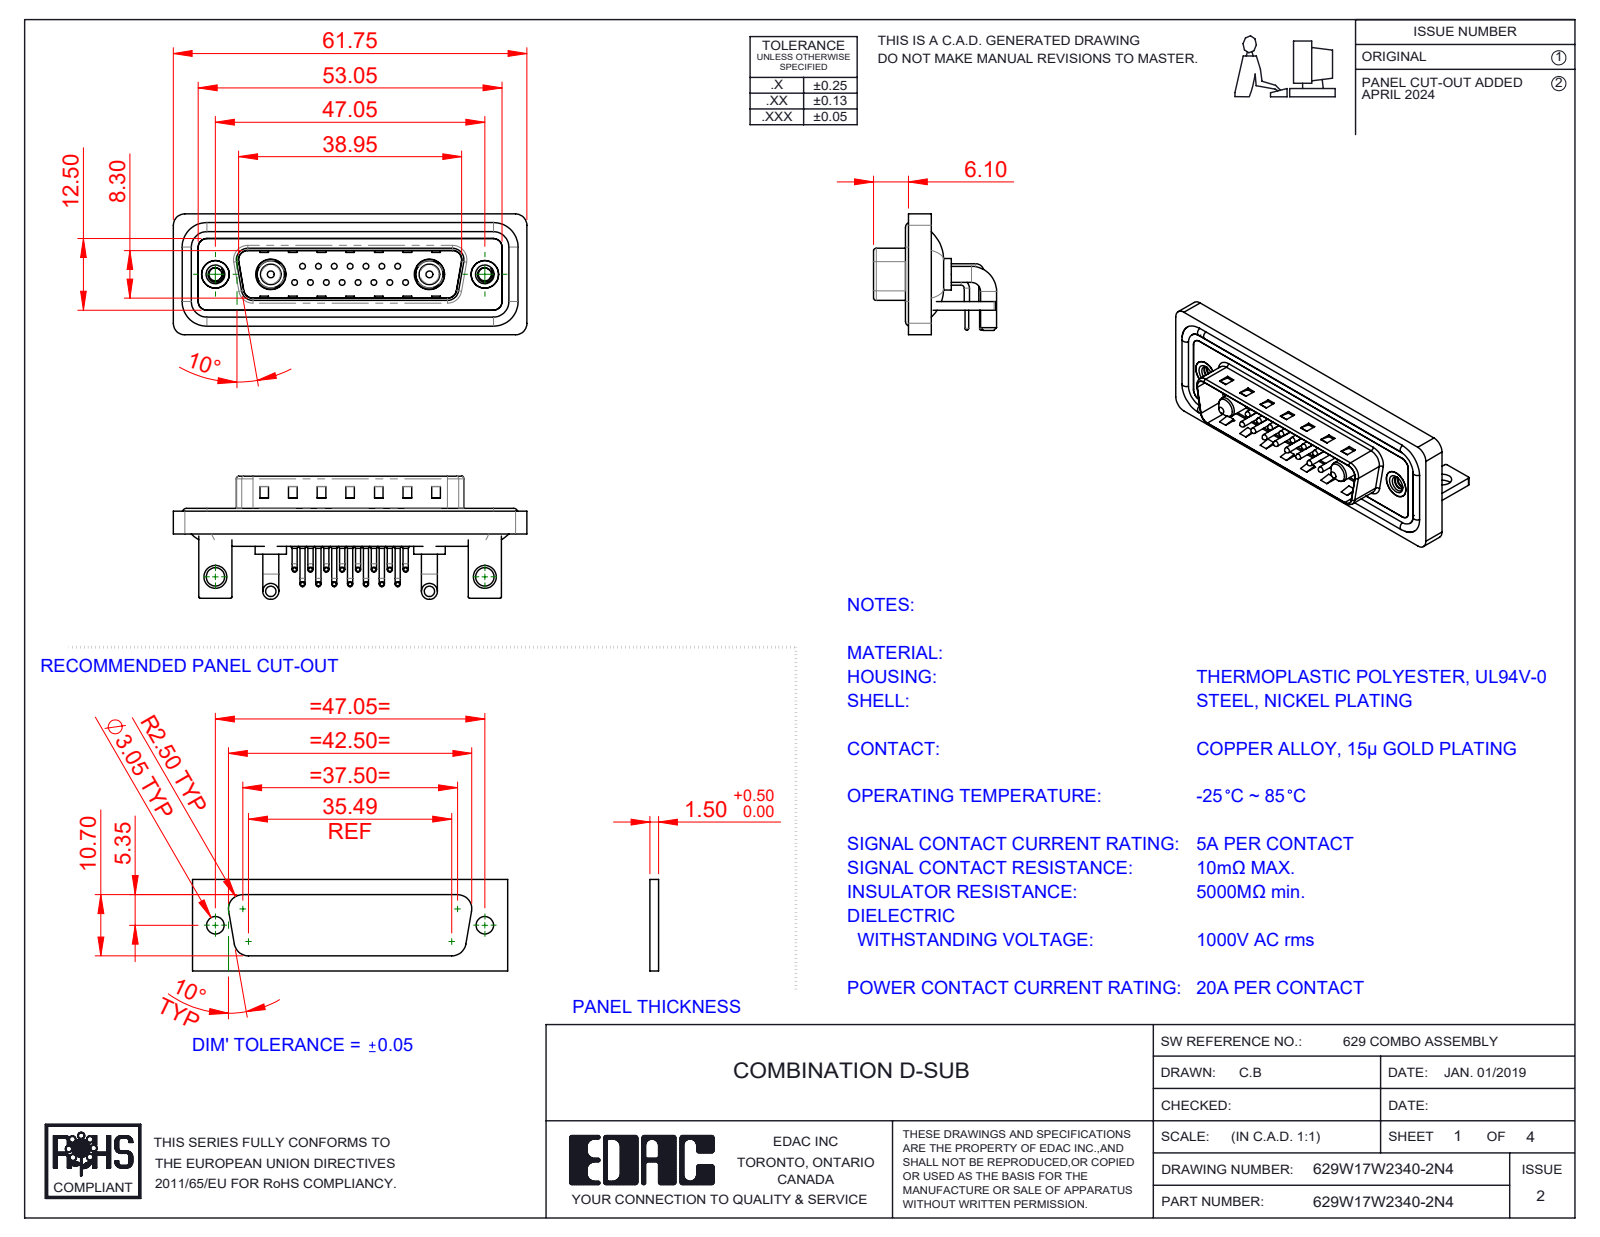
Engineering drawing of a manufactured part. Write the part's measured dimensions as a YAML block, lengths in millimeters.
part_name: "629Combo Shell Front_25 Contacts; 629Combo Waterproof Housing_25 Contacts; 629Combo Contact Row 1; 629Combo Stabilizer Bracket (+6 more)"
step_written_by: "SolidWorks 2023 (CONFIG_CONTROL_DESIGN)"
units: millimeters
bodies: {solids: 28, faces: 2259, planar: 1209, cylindrical: 788, other: 262}
overall_size: [61.75, 21.5, 21.1]
volume: 7790
surface_area: 13188
round_holes:
  - {diameter: 0.75, count: 15}
  - {diameter: 1.6, count: 15}
  - {diameter: 2, count: 15}
  - {diameter: 2.26, count: 2}
  - {diameter: 3.2, count: 2}
  - {diameter: 4, count: 2}
  - {diameter: 4.8, count: 2}
  - {diameter: 4.85, count: 2}
  - {diameter: 5, count: 2}
  - {diameter: 5.3, count: 2}
round_bosses_or_shafts:
  - {diameter: 0.9, count: 30}
  - {diameter: 1.5, count: 15}
  - {diameter: 1, count: 15}
  - {diameter: 0.65, count: 15}
  - {diameter: 2.8, count: 4}
  - {diameter: 1.6, count: 4}
  - {diameter: 5.5, count: 2}
  - {diameter: 5.2, count: 2}
partial_cylinders:
  - {radius: 2, count: 19}
  - {radius: 1.5, count: 18}
  - {radius: 0.25, count: 16}
  - {radius: 1.01, count: 15}
  - {radius: 0.5, count: 9}
  - {radius: 1.6, count: 8}
  - {radius: 0.6, count: 4}
  - {radius: 0.65, count: 4}
face_to_face_distances: [0.4, 0.8, 1.5, 2.1, 2.9, 1.1, 4.1, 1.6, 4.5, 3.7]
hole_center_spacings: [3.16, 2.77, 5.54, 8.31, 5.04, 7.49, 11.08, 5.03]
